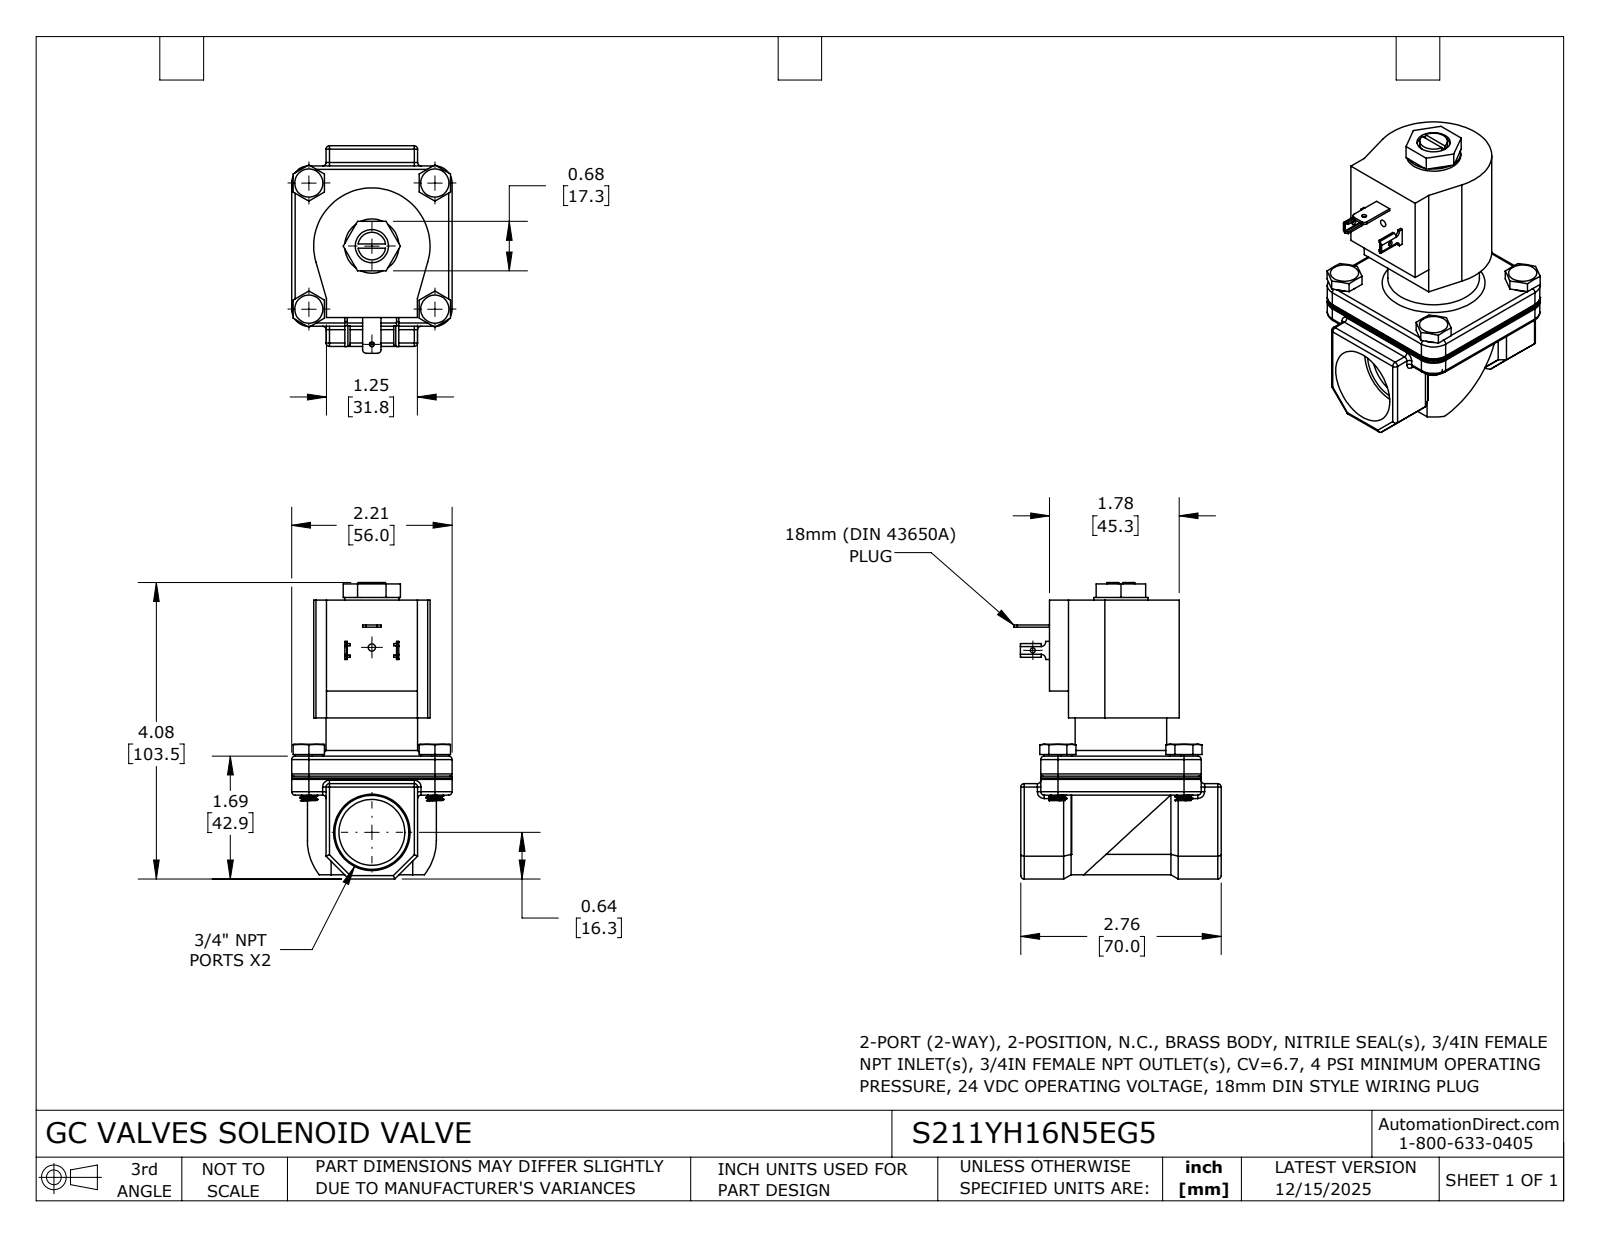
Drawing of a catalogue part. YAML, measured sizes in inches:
part_name: "S211YH16N5EG5"
step_written_by: "SolidWorks 2024 (CONFIG_CONTROL_DESIGN)"
units: inches
bodies: {solids: 3, faces: 348, planar: 168, cylindrical: 120, other: 60}
overall_size: [4.075, 2.851, 2.205]
volume: 9.987
surface_area: 44.97
round_holes:
  - {diameter: 0.066, count: 1}
  - {diameter: 0.067, count: 1}
  - {diameter: 0.1, count: 1}
  - {diameter: 0.456, count: 1}
  - {diameter: 0.906, count: 1}
round_bosses_or_shafts:
  - {diameter: 0.388, count: 4}
  - {diameter: 0.244, count: 4}
  - {diameter: 1.26, count: 1}
  - {diameter: 0.746, count: 1}
  - {diameter: 0.38, count: 1}
partial_cylinders:
  - {radius: 0.047, count: 34}
  - {radius: 0.006, count: 4}
  - {radius: 0.031, count: 4}
  - {radius: 0.041, count: 4}
  - {radius: 0.234, count: 4}
  - {radius: 0.236, count: 4}
  - {radius: 0.05, count: 2}
  - {radius: 0.06, count: 2}
face_to_face_distances: [0.059, 2.143, 0.472, 1.732, 0.537, 2.68, 2.205, 0.523, 1.094, 1.631]
hole_center_spacings: [1.35, 2.541]
